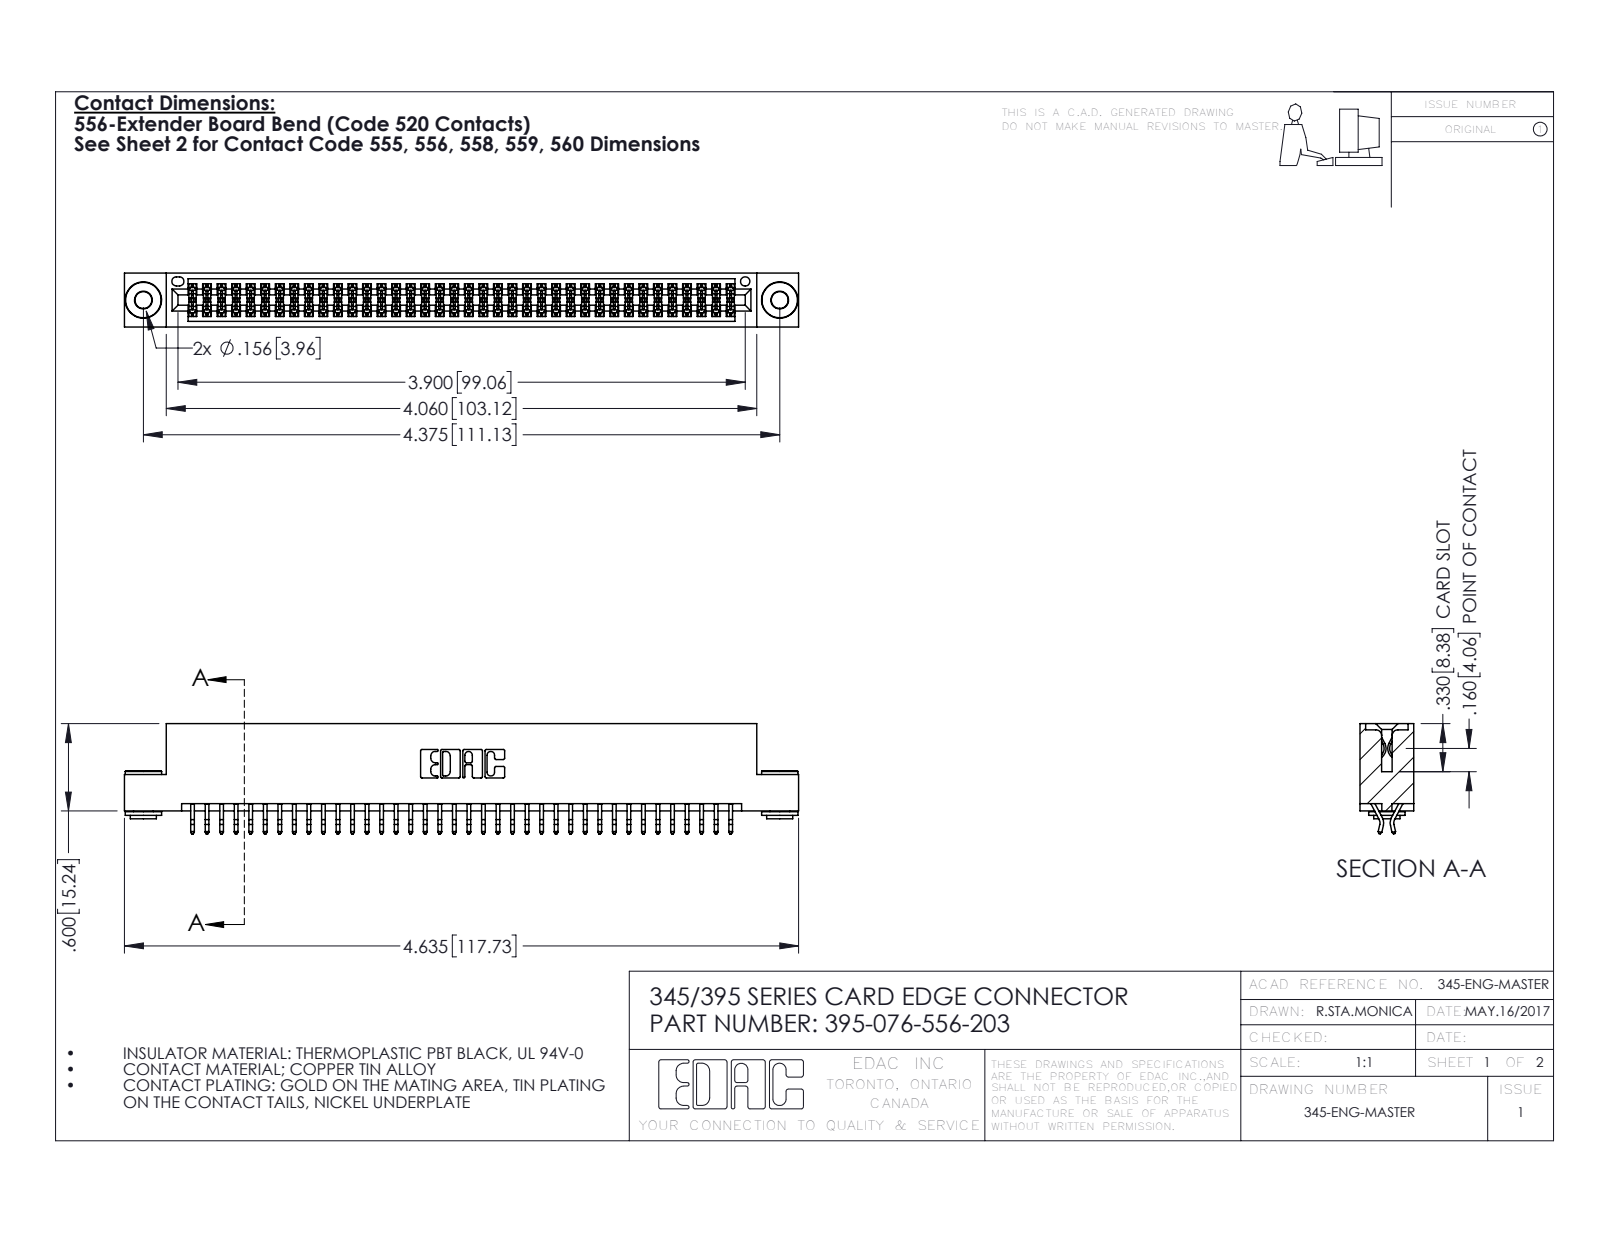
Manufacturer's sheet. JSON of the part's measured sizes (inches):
{"part_name": "395-076-556-203; 345-250-002_345-250-002-102; 345 Part_Flush Mounting Lugs - 0.156 Dia-TH; 345-292-001_556 Tail", "step_written_by": "SolidWorks 2016 (CONFIG_CONTROL_DESIGN)", "units": "inches", "bodies": {"solids": 79, "faces": 4420, "planar": 2902, "cylindrical": 1510, "other": 8}, "overall_size": [4.635, 0.757, 0.37], "volume_in3": 0.697, "surface_area_in2": 26.25, "round_holes": [[0.116, 2], [0.156, 2], [0.064, 1]], "round_bosses_or_shafts": [[0.25, 2], [0.18, 2], [0.136, 2]], "partial_cylinders_radius": [[0.006, 114], [0.01, 22], [0.007, 6], [0.031, 6], [0.026, 3], [0.01, 2], [0.014, 2], [0.019, 2]], "face_to_face_distances": [0.072, 0.298, 0.2, 0.37, 0.025, 0.098, 0.272, 0.225, 0.175, 0.149], "hole_center_spacings": [0.27, 4.139, 4.375]}
